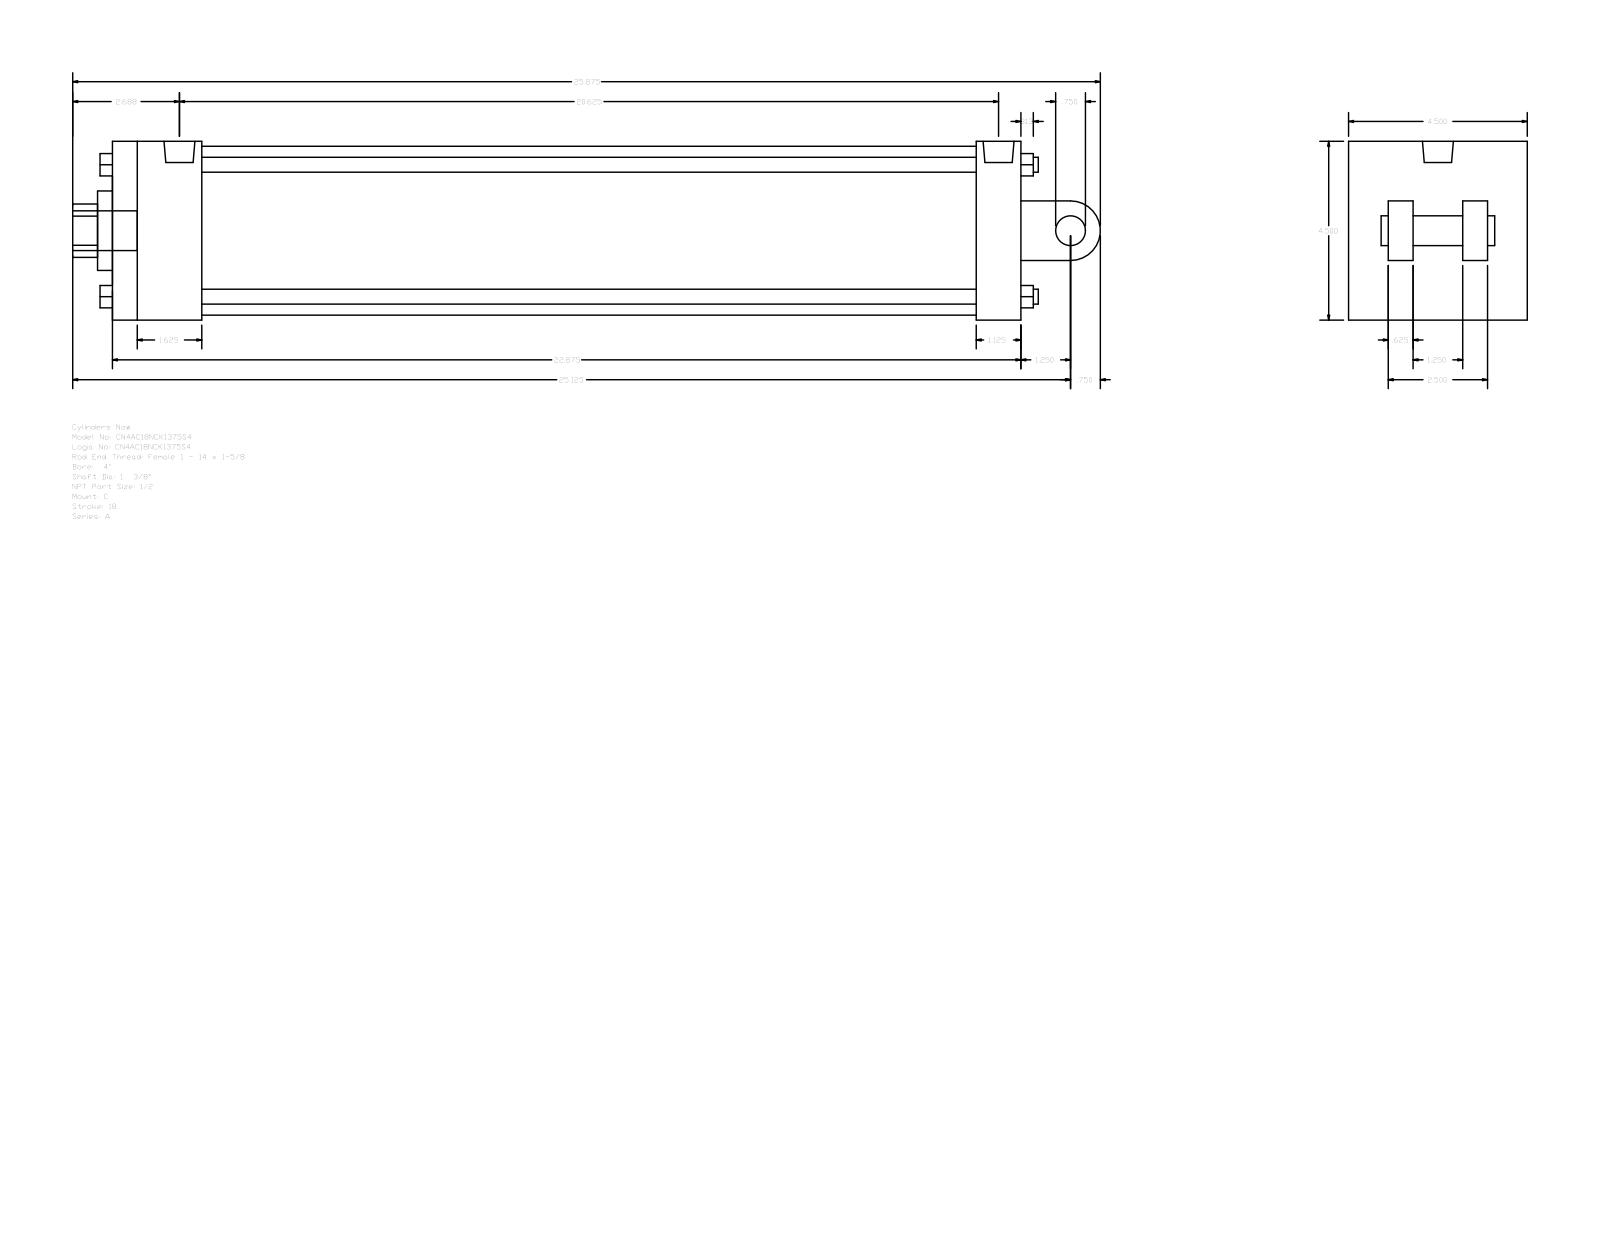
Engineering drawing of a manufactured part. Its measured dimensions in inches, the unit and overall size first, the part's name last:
Units: inches
Overall size (bounding box): 25.875 × 4.5 × 4.5
Round holes (diameter × count): ⌀0.344 ×2, ⌀0.778 ×1, ⌀1.375 ×1, ⌀2 ×1, ⌀4.25 ×1
Round bosses / shafts (diameter × count): ⌀0.375 ×4, ⌀0.344 ×2, ⌀1 ×1, ⌀0.778 ×1, ⌀0.75 ×1
Partial cylindrical surfaces — rounded edges, fillets, slot ends (radius × count): R0.672 ×1, R0.75 ×1
Main face-to-face distances: 4.5, 22.875, 2.875, 1.125, 21.75, 2.25, 19.5, 20.625, 0.625, 1.625
Hole centre spacings: 0.125
Bodies: 0 solids, 135 faces (102 planar, 33 cylindrical, 0 other)
Part name (STEP PRODUCT): A_C__0400_1.375
STEP written by: GSSL Pune (CONFIG_CONTROL_DESIGN)
